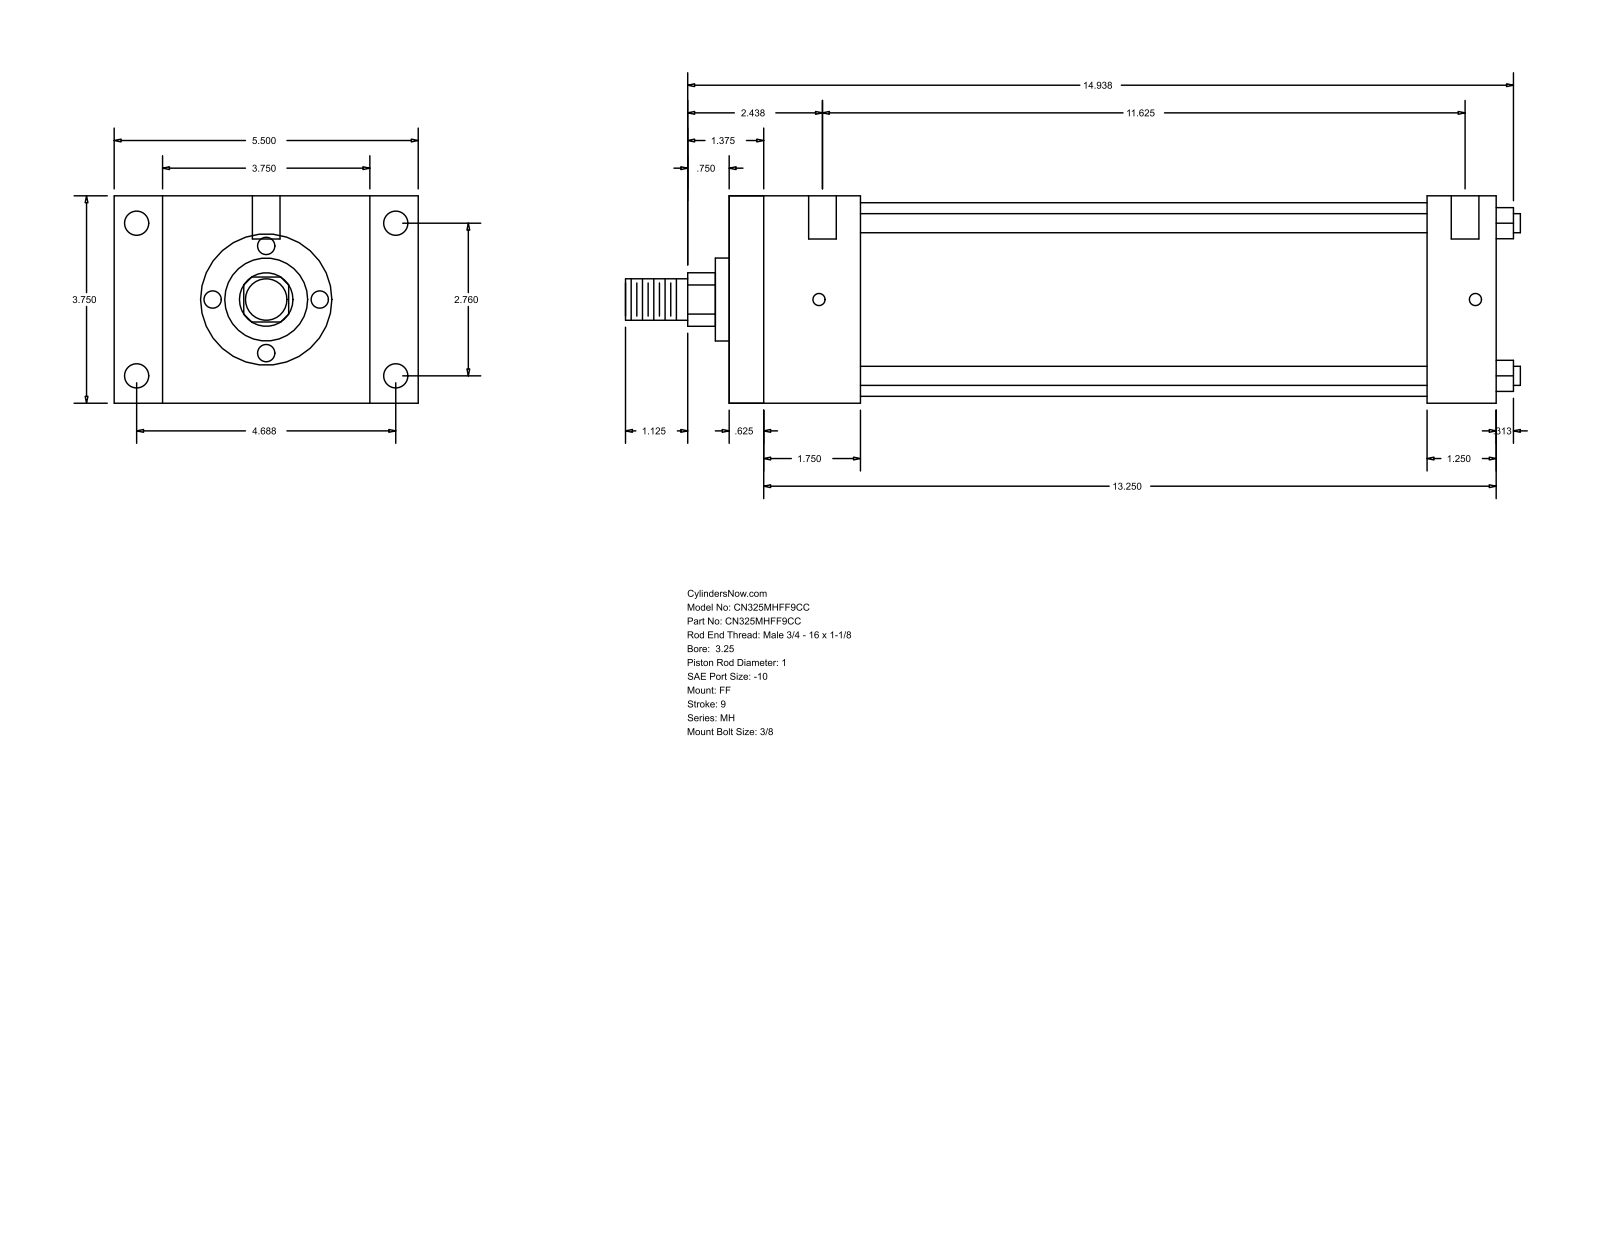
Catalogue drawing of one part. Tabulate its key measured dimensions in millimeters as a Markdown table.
| quantity | value |
| --- | --- |
| part name | MH_FF__0325_1 |
| STEP written by | GSSL Pune (CONFIG_CONTROL_DESIGN) |
| units | millimeters |
| bodies | 0 solids, 92 faces (64 planar, 28 cylindrical, 0 other) |
| overall size | 411.16 × 139.7 × 95.25 |
| round holes (diameter × count) | 5.56 × 4, 11.13 × 4, 12.7 × 2 |
| round bosses / shafts (diameter × count) | 8.76 × 4, 88.9 × 1, 38.1 × 1, 25.4 × 1, 19.05 × 1 |
| partial cylindrical surfaces (radius × count) | 12.29 × 1 |
| main face-to-face distances | 95.24, 352.43, 15.87, 336.56, 22.23, 117.47, 320.68, 304.81, 31.75, 60.33 |
| hole center spacings | 70.1, 119.06, 138.16, 301.62, 1.58, 4.76, 295.28, 296.86 |
